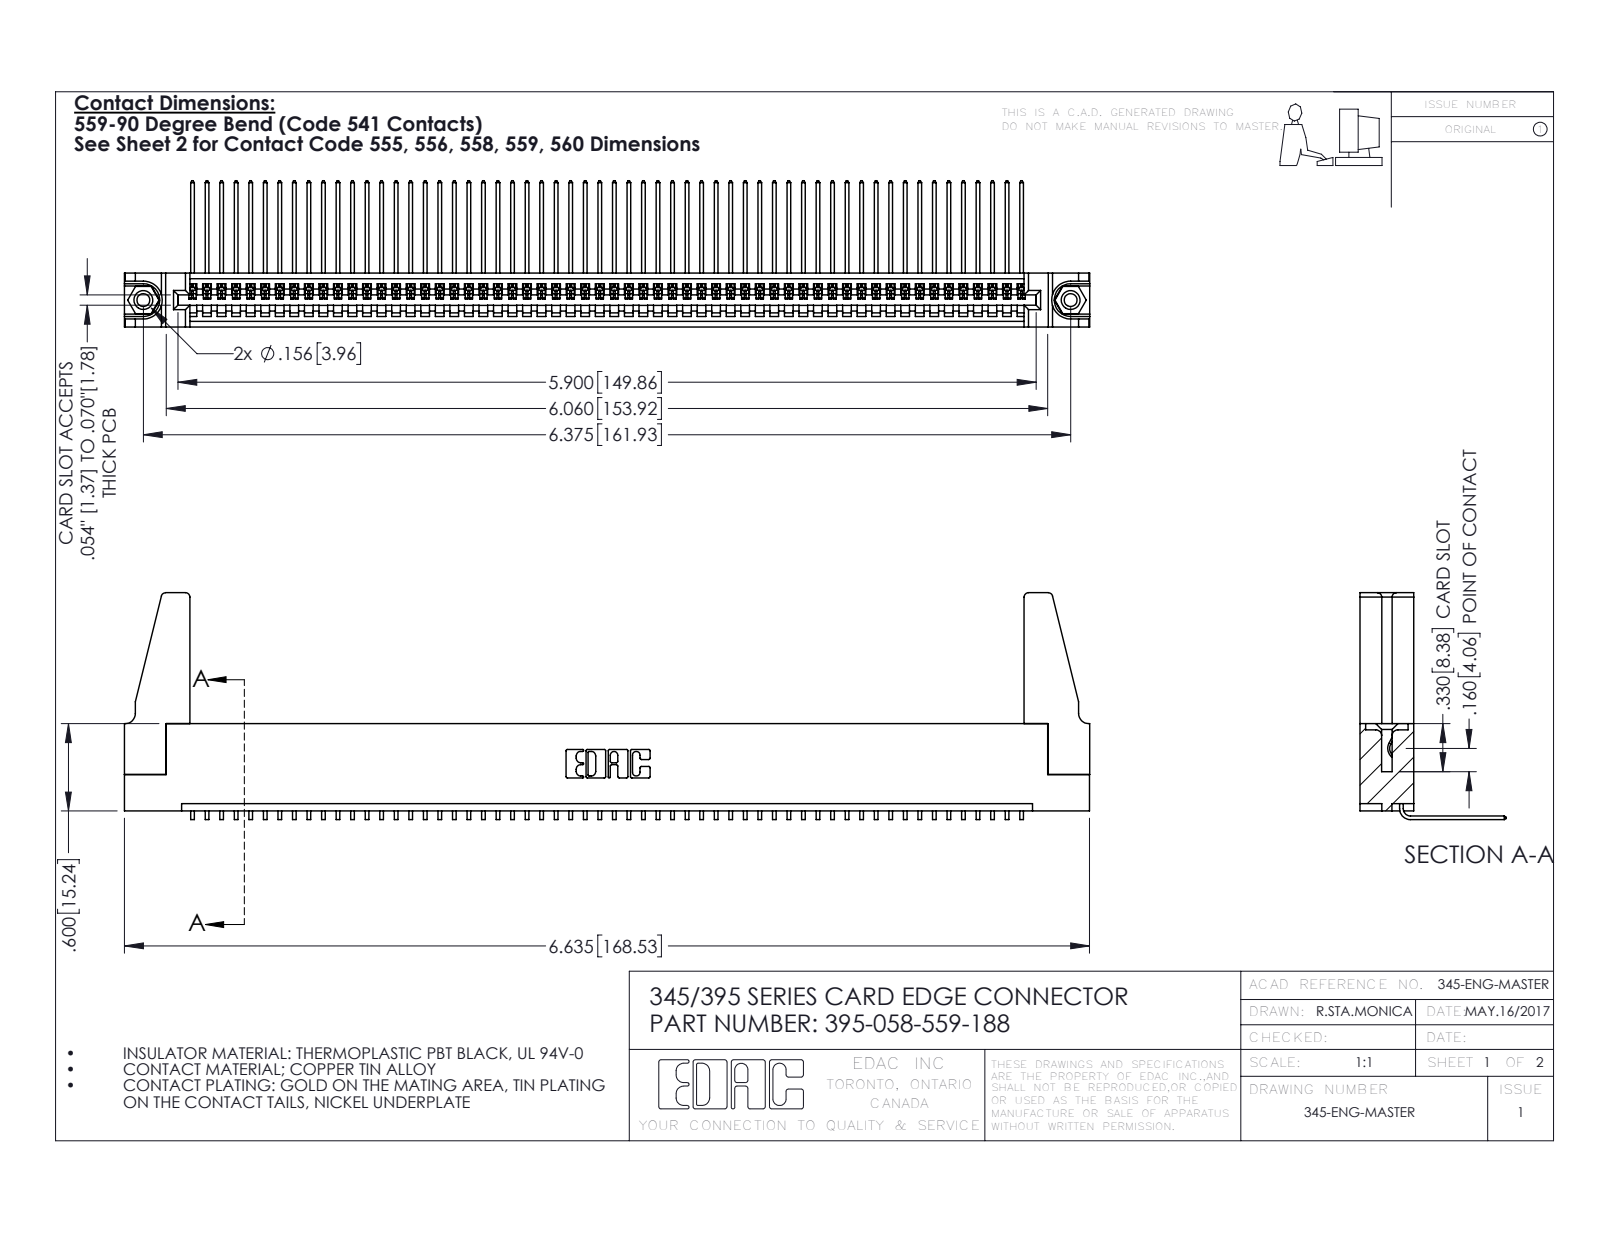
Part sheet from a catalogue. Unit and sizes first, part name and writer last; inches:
Units: inches
Overall size (bounding box): 6.636 × 1.559 × 1.005
Round holes (diameter × count): ⌀0.089 ×2, ⌀0.125 ×2, ⌀0.156 ×2, ⌀0.064 ×1
Round bosses / shafts (diameter × count): ⌀0.155 ×2
Partial cylindrical surfaces — rounded edges, fillets, slot ends (radius × count): R0.006 ×116, R0.01 ×22, R0.03 ×8, R0.007 ×6, R0.031 ×6, R0.026 ×3, R0.031 ×2, R0.04 ×2
Main face-to-face distances: 0.072, 0.298, 0.37, 0.2, 0.098, 0.272, 0.025, 0.225, 0.149, 0.072
Hole centre spacings: 0.27, 6.139, 6.375
Volume: 1.195 in³ · Surface area: 40.59 in²
Bodies: 63 solids, 3730 faces (2588 planar, 1126 cylindrical, 16 other)
Part name (STEP PRODUCT): 345-292-001_558 559 Tail - 1; 395-058-559-188; 345-220-078_345-220-088; 345 Part_Flush Mounting Lugs - 0.156 Dia-TH (+1 more)
STEP written by: SolidWorks 2016 (CONFIG_CONTROL_DESIGN)
